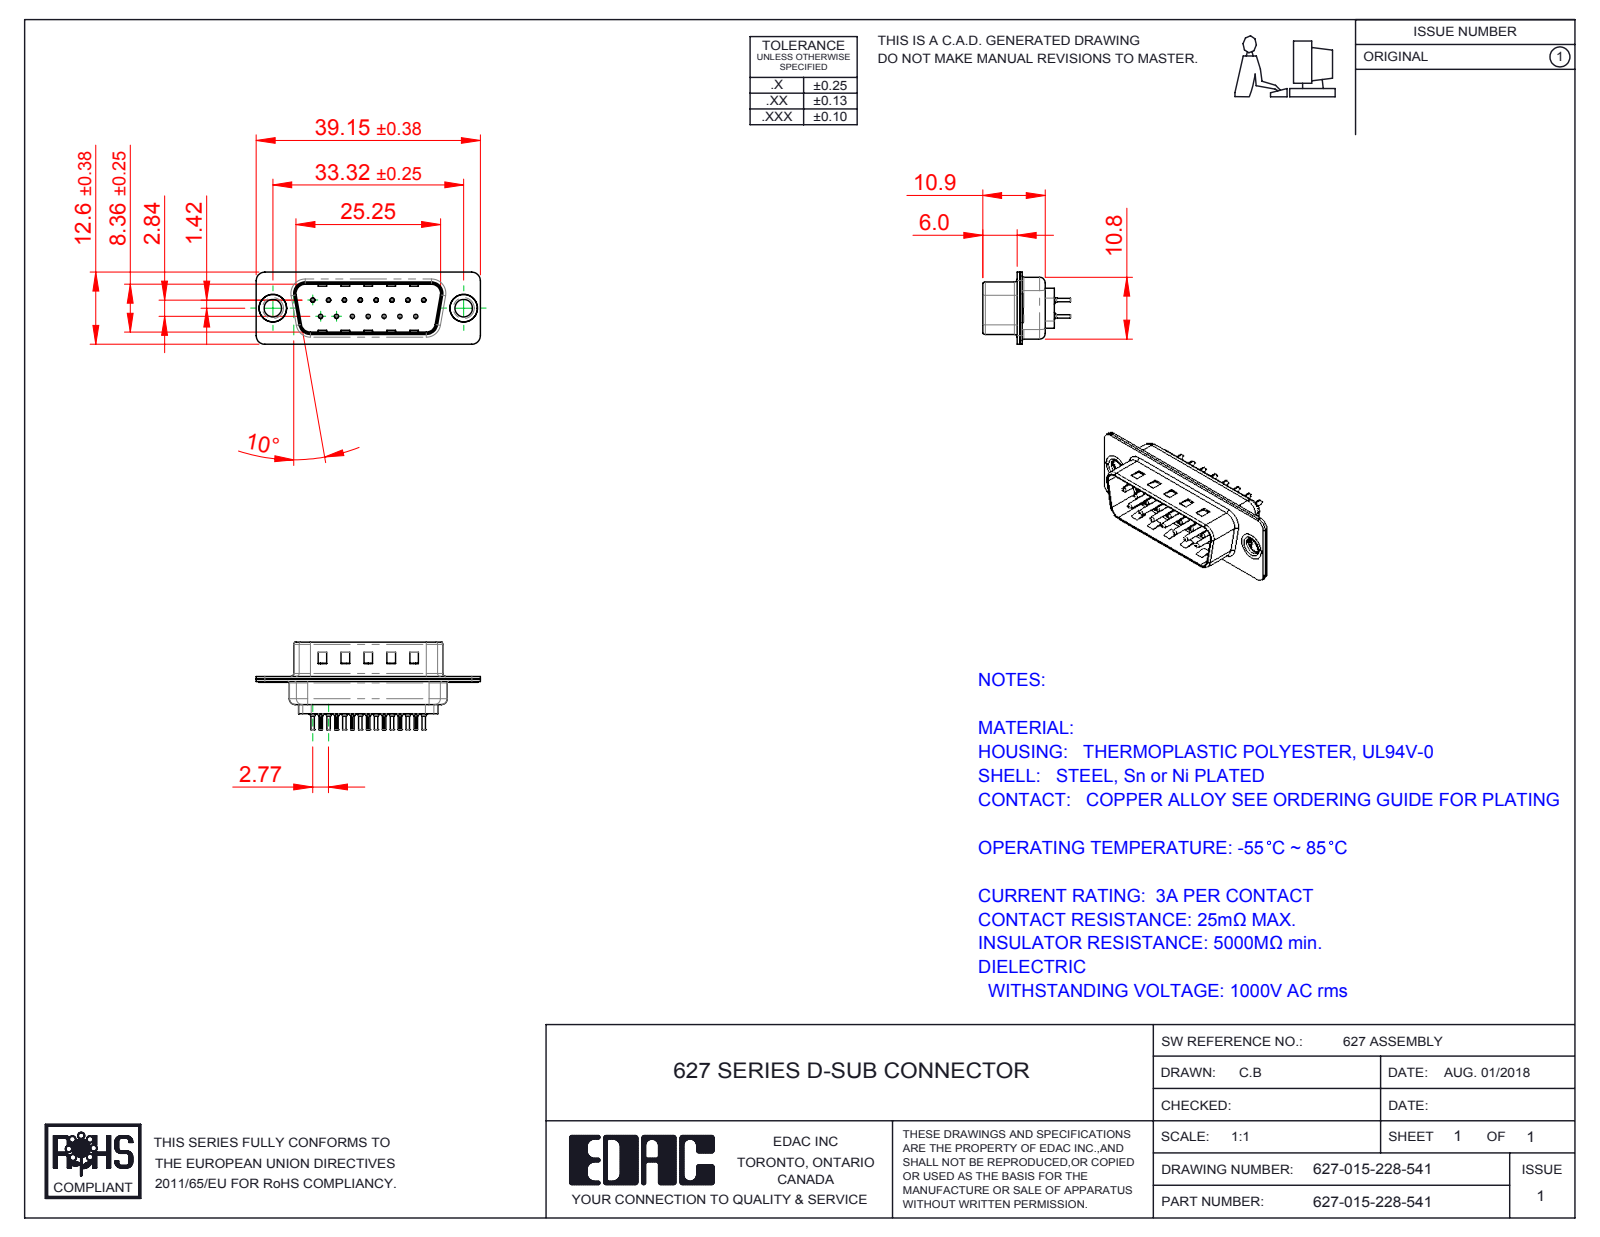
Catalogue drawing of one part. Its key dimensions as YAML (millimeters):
part_name: "627 Contact Row 1_28L; 627 Thru Hole Rivet; 627 Shell Front_15 Contacts; 627 Housing_15 LP (+3 more)"
step_written_by: "SolidWorks 2016 (CONFIG_CONTROL_DESIGN)"
units: millimeters
bodies: {solids: 20, faces: 1784, planar: 499, cylindrical: 672, other: 613}
overall_size: [39.15, 15.3, 12.6]
volume: 1745
surface_area: 5161
round_holes:
  - {diameter: 0.2, count: 15}
  - {diameter: 0.35, count: 15}
  - {diameter: 1.1, count: 15}
  - {diameter: 1.6, count: 15}
  - {diameter: 3.05, count: 2}
  - {diameter: 4, count: 2}
  - {diameter: 4.8, count: 2}
round_bosses_or_shafts:
  - {diameter: 2, count: 15}
  - {diameter: 1.5, count: 15}
  - {diameter: 0.75, count: 15}
  - {diameter: 0.6, count: 15}
  - {diameter: 5, count: 2}
  - {diameter: 4.9, count: 2}
  - {diameter: 3.55, count: 2}
partial_cylinders:
  - {radius: 0.1, count: 30}
  - {radius: 1.5, count: 16}
  - {radius: 2, count: 12}
  - {radius: 0.5, count: 8}
  - {radius: 1.6, count: 8}
  - {radius: 0.25, count: 4}
  - {radius: 0.6, count: 4}
  - {radius: 0.65, count: 4}
face_to_face_distances: [0.4, 0.45, 0.9, 0.82, 9.58, 8.76, 1.5, 1.4, 0.5, 6.5]
hole_center_spacings: [3.16, 2.77, 5.54, 8.31, 11.08, 5.03, 5.04, 7.48]
